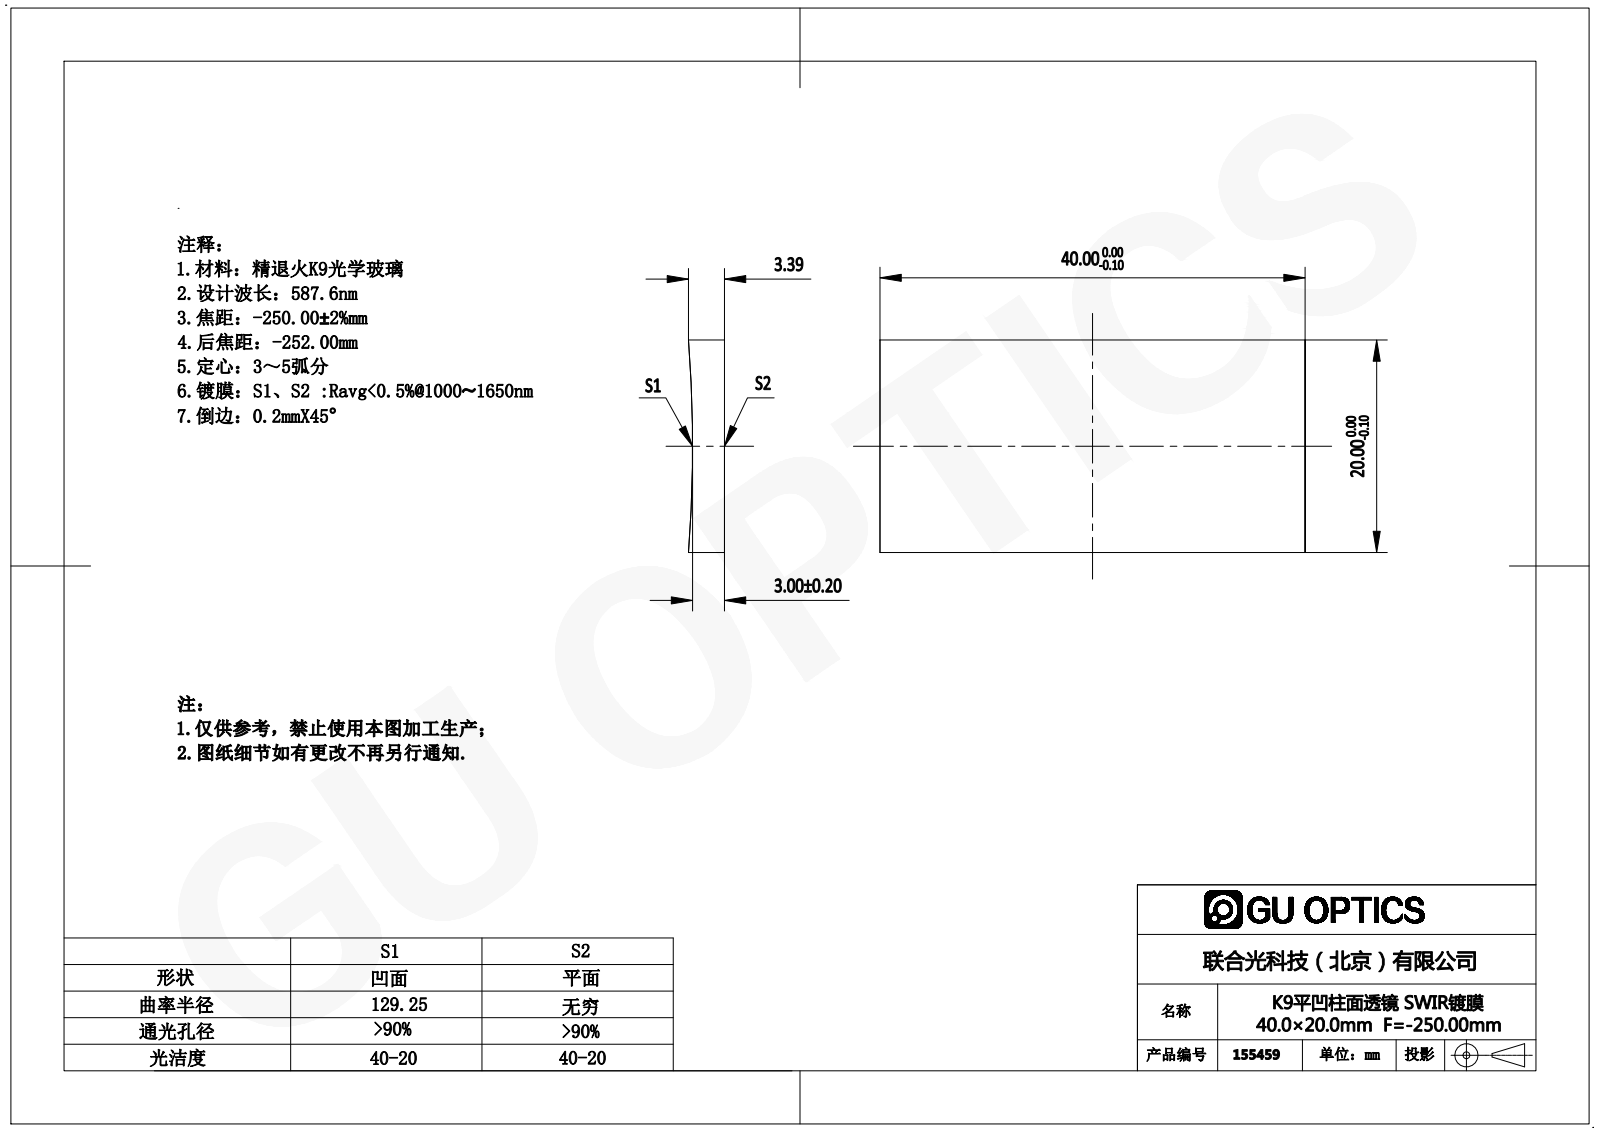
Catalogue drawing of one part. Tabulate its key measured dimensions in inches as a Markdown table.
| quantity | value |
| --- | --- |
| part name | 155360 |
| STEP written by | SolidWorks 2016 (AUTOMOTIVE_DESIGN) |
| units | inches |
| bodies | 1 solid, 6 faces (5 planar, 1 cylindrical, 0 other) |
| overall size | 1.575 × 0.787 × 0.133 |
| volume | 0.153 in³ |
| surface area | 3.095 in² |
| partial cylindrical surfaces (radius × count) | 5.089 × 1 |
| main face-to-face distances | 0.787, 1.575 |
